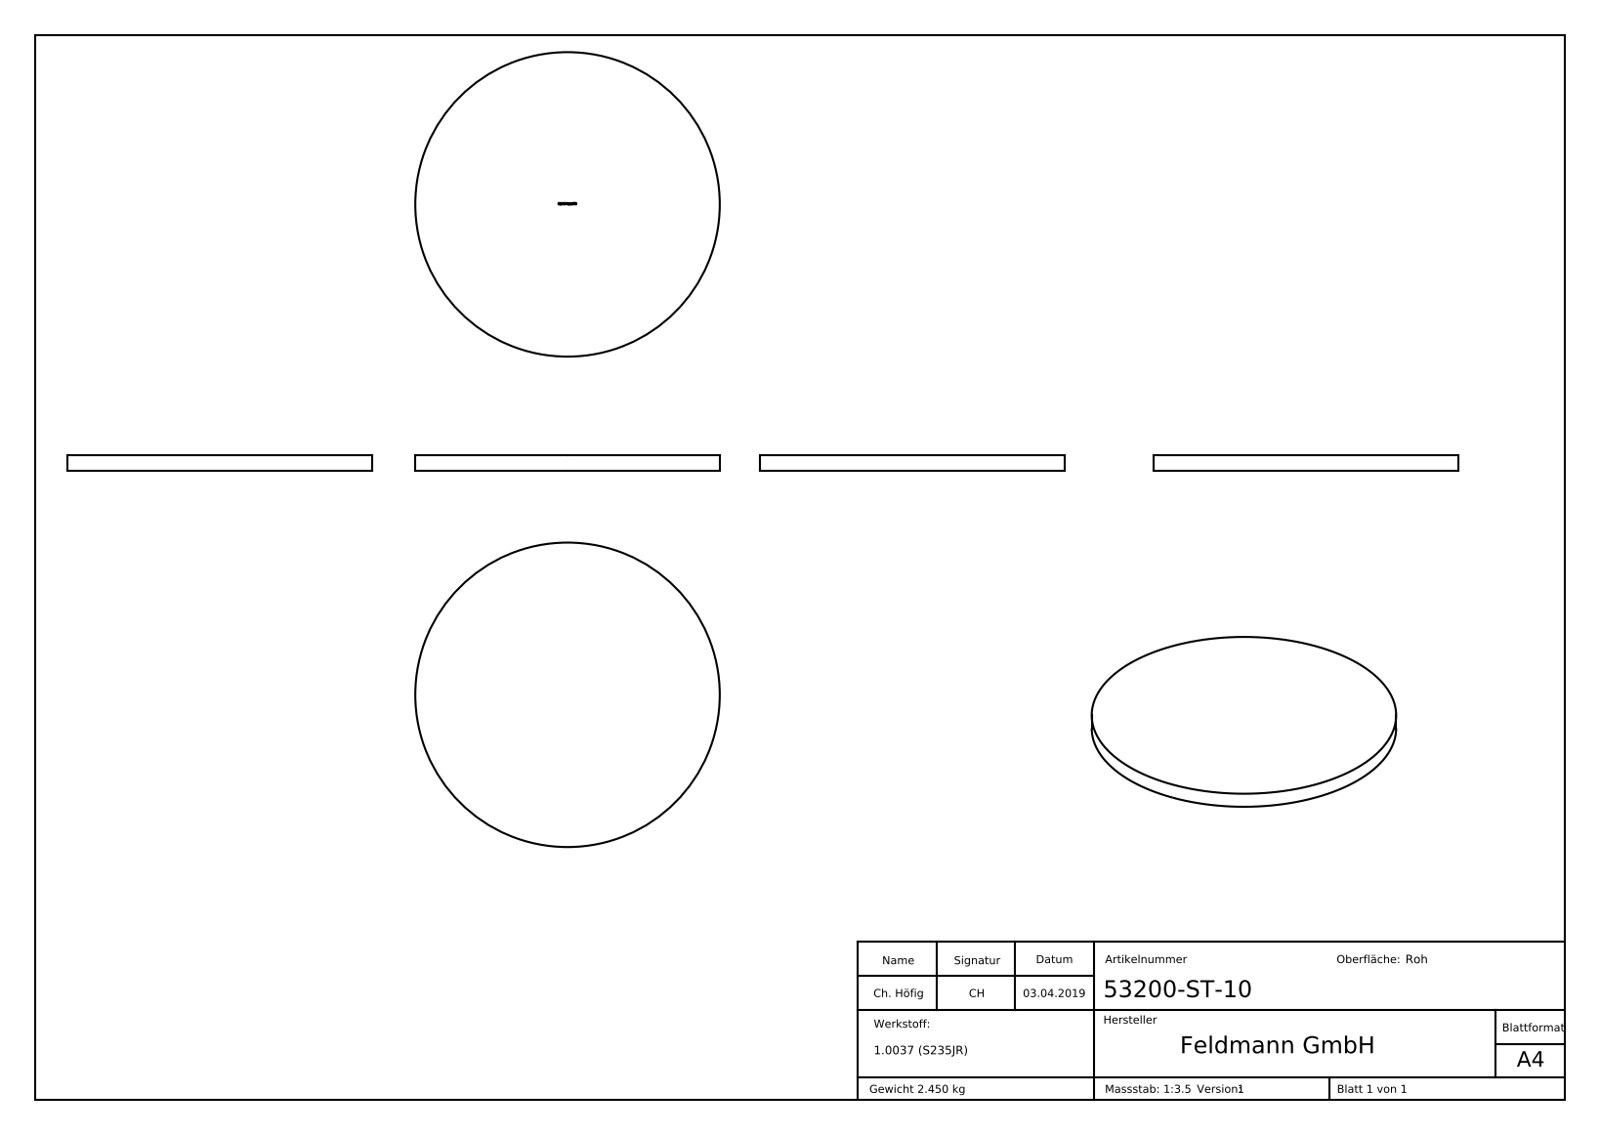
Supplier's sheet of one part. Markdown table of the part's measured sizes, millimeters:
| quantity | value |
| --- | --- |
| part name | 53200-ST-10 |
| STEP written by | SolidWorks 2015 (CONFIG_CONTROL_DESIGN) |
| units | millimeters |
| bodies | 1 solid, 240 faces (120 planar, 2 cylindrical, 118 other) |
| overall size | 200 × 200 × 10 |
| volume | 314 159 mm³ |
| surface area | 69 121 mm² |
| round bosses / shafts (diameter × count) | 200 × 1 |
| main face-to-face distances | 10, 9.9, 1.78, 0.91, 0.75, 0.98, 0.79, 0.44, 9.39, 1.21 |
